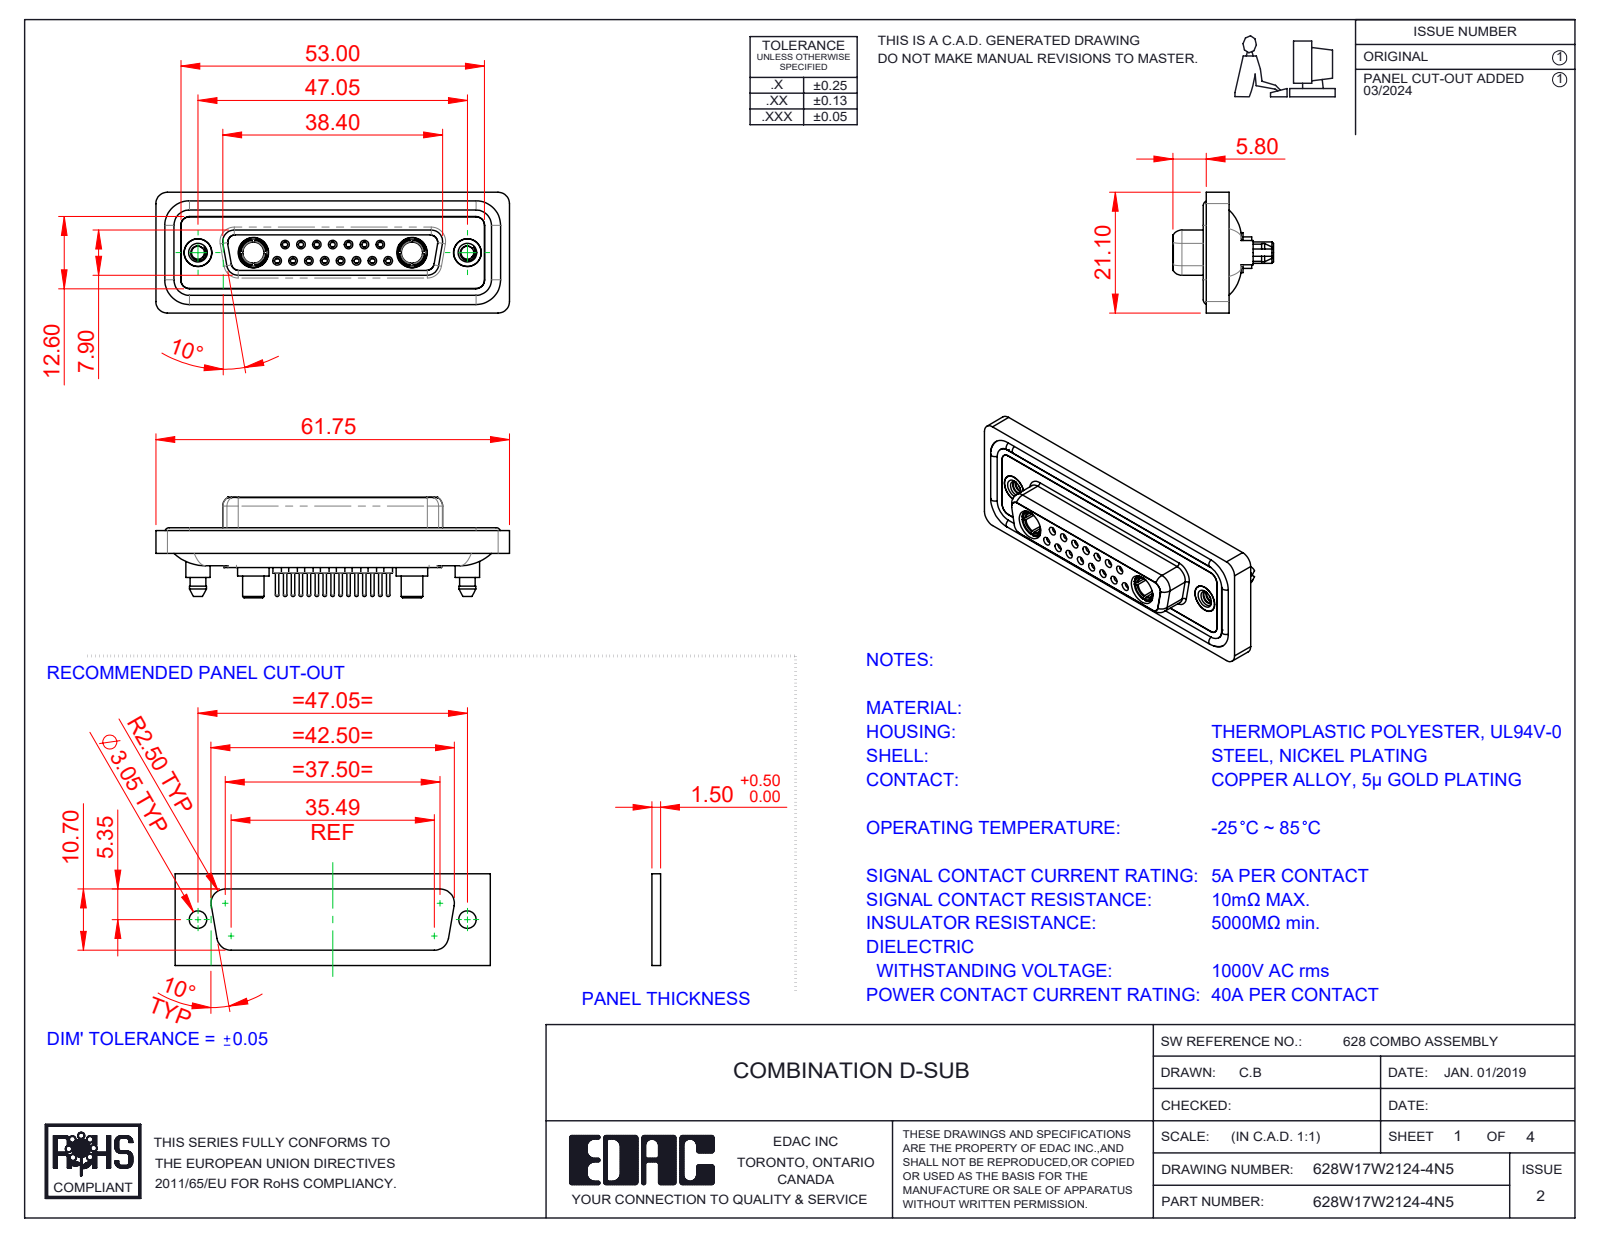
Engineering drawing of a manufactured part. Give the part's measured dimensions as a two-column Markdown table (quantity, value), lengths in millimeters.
| quantity | value |
| --- | --- |
| part name | 628Combo Contact Row 2_24; 628Combo Shell Rear_25 Contacts; 628Combo Threaded Boardlock_5; Power Socket_40A S (+5 more) |
| STEP written by | SolidWorks 2023 (CONFIG_CONTROL_DESIGN) |
| units | millimeters |
| bodies | 26 solids, 1409 faces (404 planar, 551 cylindrical, 454 other) |
| overall size | 61.75 × 21.1 × 17.55 |
| volume | 8 495 mm³ |
| surface area | 14 210 mm² |
| round holes (diameter × count) | 0.9 × 15, 1.1 × 15, 1.5 × 15, 2 × 15, 1.6 × 8, 1.7 × 7, 4.85 × 4, 2.26 × 2, 3.7 × 2, 4 × 2, 4.05 × 2, 5 × 2 |
| round bosses / shafts (diameter × count) | 2.2 × 15, 0.6 × 15, 1.6 × 11, 5.5 × 2, 5.4 × 2, 5.2 × 2, 4.96 × 2, 4.95 × 2 |
| partial cylindrical surfaces (radius × count) | 1.5 × 24, 2 × 18, 1.6 × 10, 1.35 × 8, 0.25 × 4, 0.5 × 4, 0.6 × 4, 0.65 × 4 |
| main face-to-face distances | 0.4, 1.8, 7.45, 5.65, 6.6, 0.5, 7.05, 1.6, 2.9, 1.1 |
| hole center spacings | 3.16, 2.77, 8.31, 5.54, 5.03, 5.04, 7.49, 11.08 |
